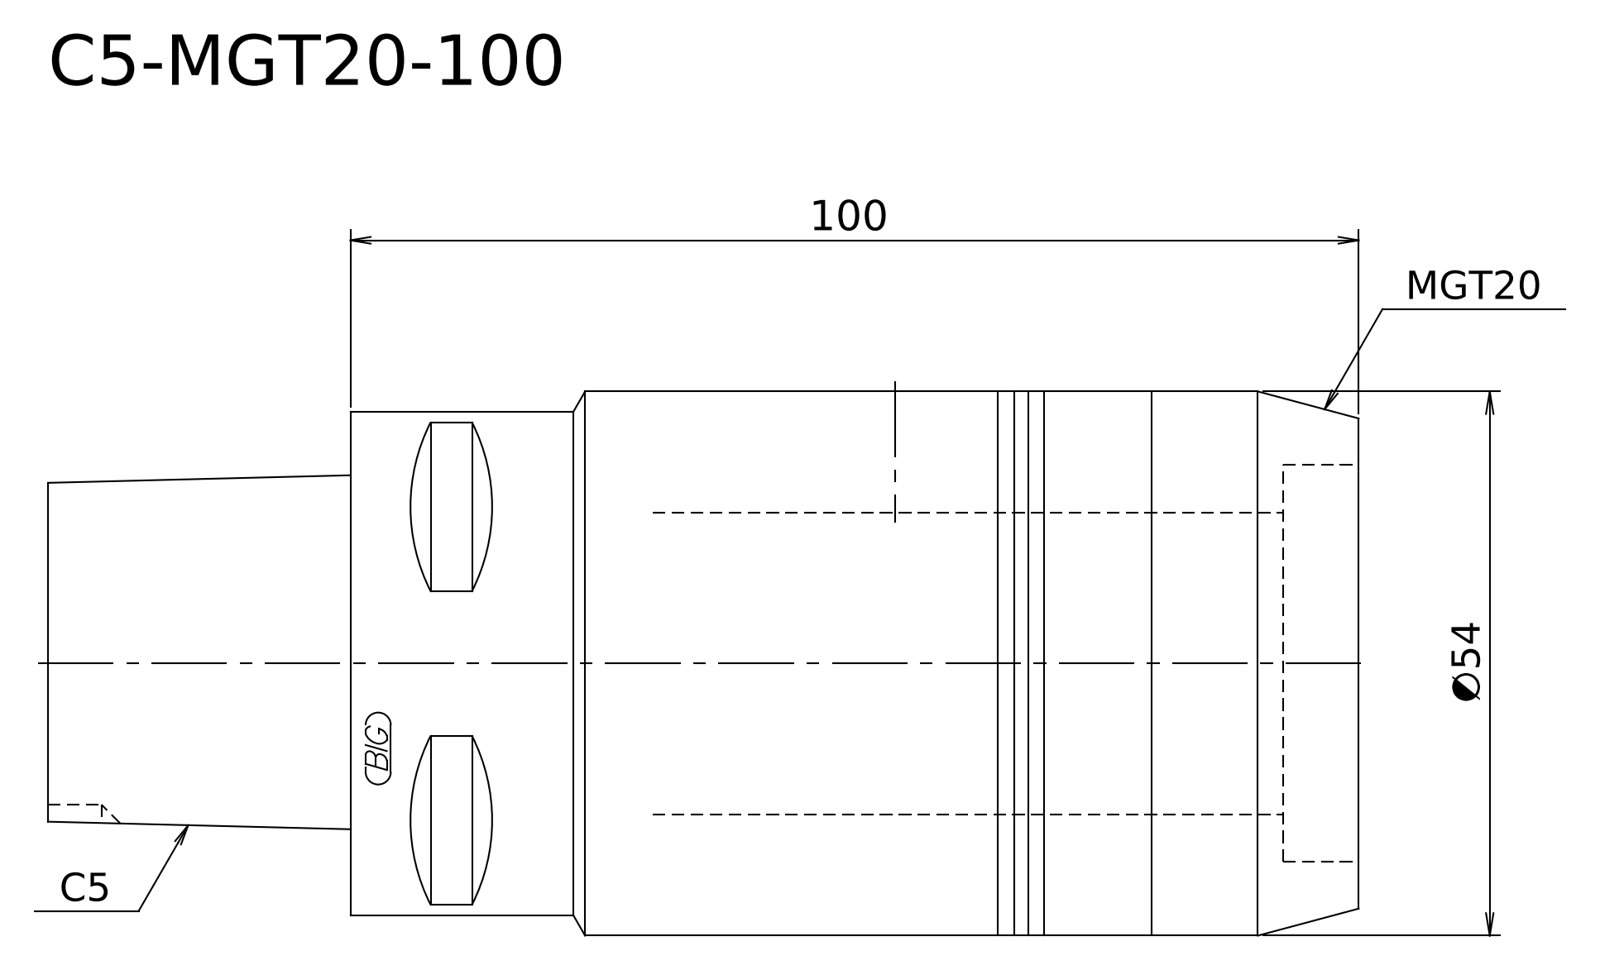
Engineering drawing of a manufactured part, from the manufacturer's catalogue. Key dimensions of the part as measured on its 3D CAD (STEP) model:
STEP written by: Kubotek KeyCreator V8.5.1 (14335) (CONFIG_CONTROL_DESIGN)
Units: millimetres
Bodies: 1 solid, 8 faces (3 planar, 2 cylindrical, 3 other)
Overall size (bounding box): 130 × 54 × 54
Volume: 246 554 mm³ · Surface area: 23 822 mm²
Round bosses / shafts (diameter × count): ⌀54 ×1, ⌀49.98 ×1
Main face-to-face distances: 100, 130, 30
